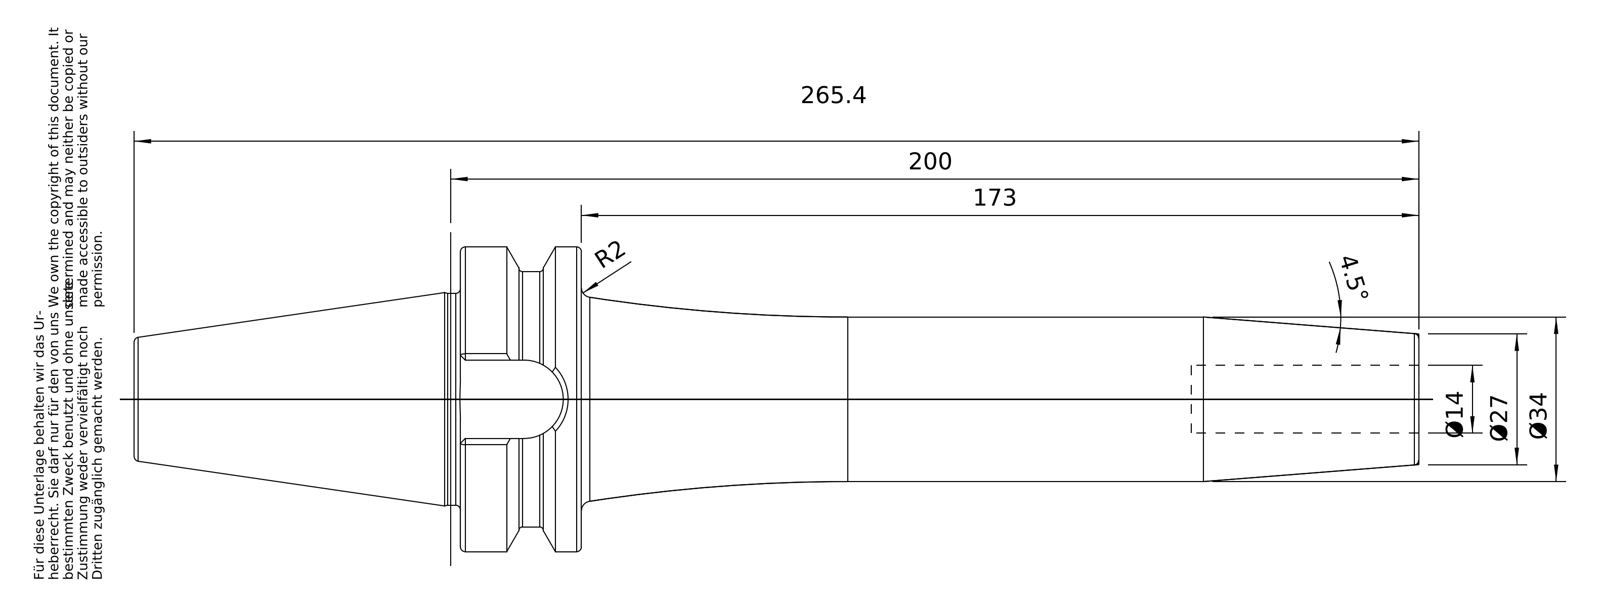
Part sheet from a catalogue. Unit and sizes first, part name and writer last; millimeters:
Units: millimetres
Overall size (bounding box): 265.4 × 62.98 × 62.98
Round holes (diameter × count): ⌀13.84 ×1, ⌀14 ×1, ⌀17.01 ×1, ⌀17.5 ×1
Round bosses / shafts (diameter × count): ⌀62.98 ×1, ⌀52.75 ×1, ⌀43.75 ×1, ⌀34 ×1, ⌀16.01 ×1
Partial cylindrical surfaces — rounded edges, fillets, slot ends (radius × count): R8.1 ×1
Main face-to-face distances: 25, 198, 173, 44.9, 151, 126, 47, 16.2, 67.4, 92.4
Volume: 277 446 mm³ · Surface area: 41 464 mm²
Bodies: 1 solid, 98 faces (26 planar, 22 cylindrical, 50 other)
Part name (STEP PRODUCT): 40-646-14
STEP written by: PRO/ENGINEER BY PARAMETRIC TECHNOLOGY CORPORATION, 2010430 (CONFIG_CONTROL_DESIGN)
